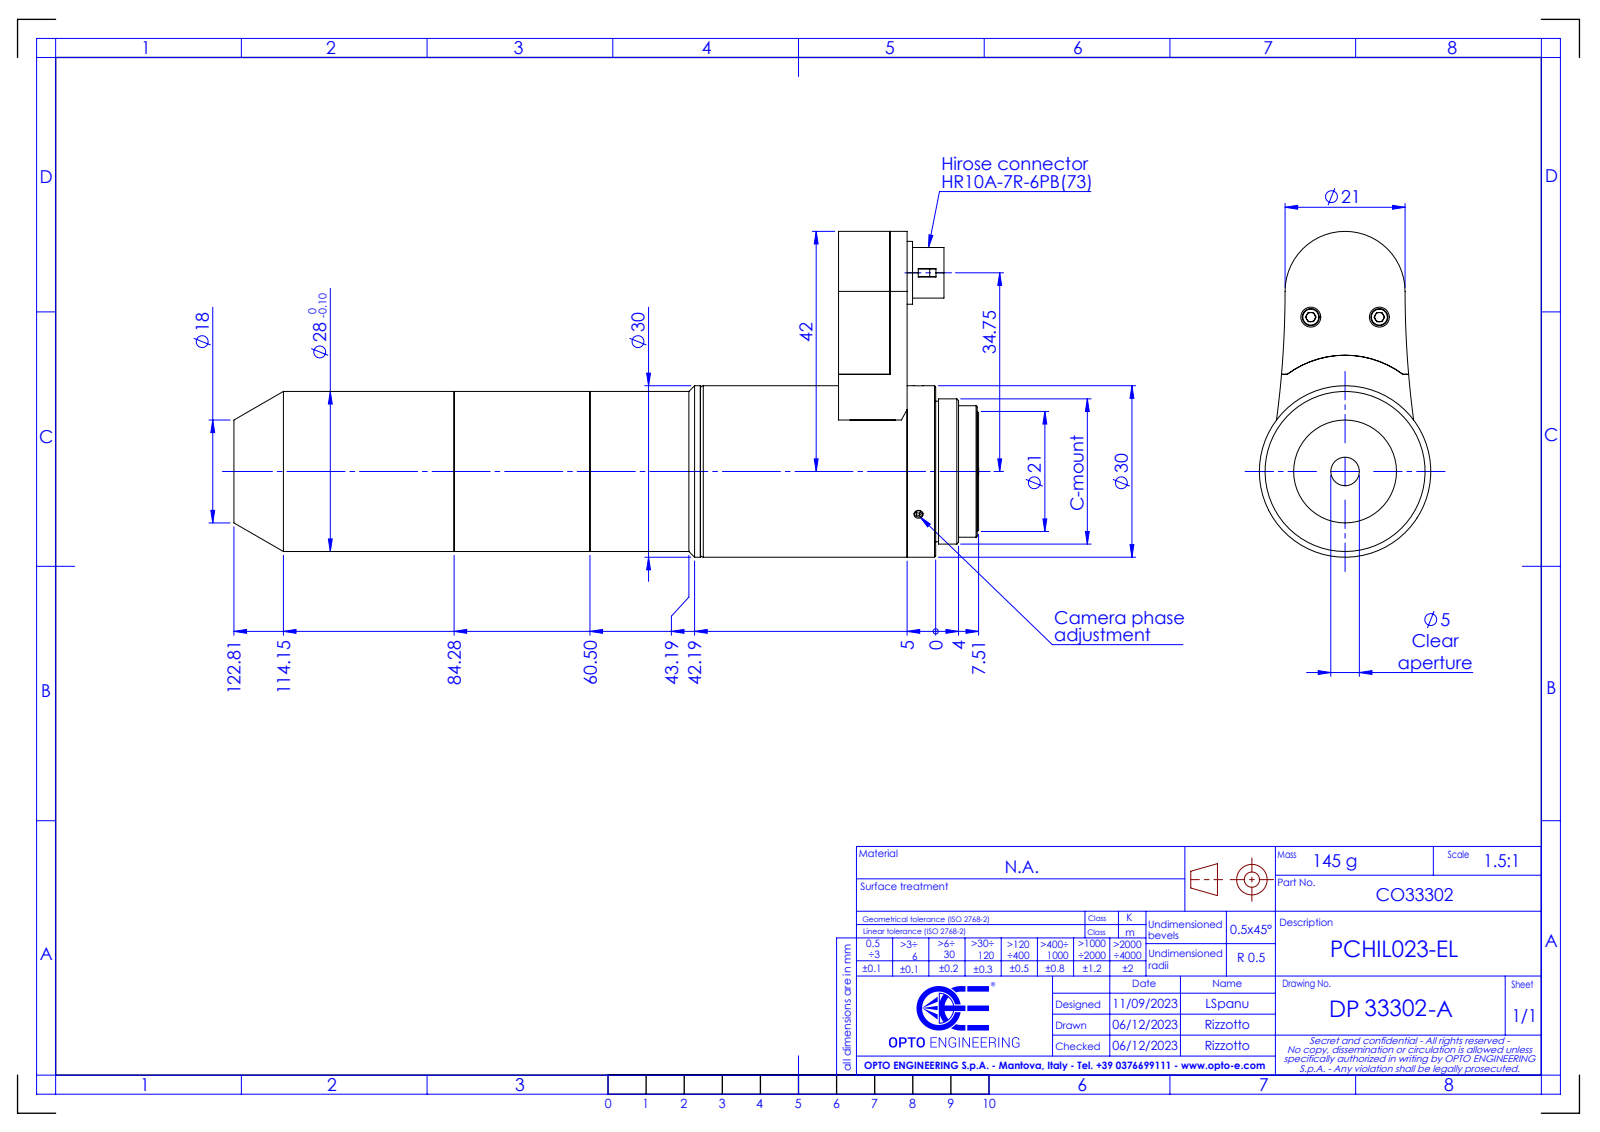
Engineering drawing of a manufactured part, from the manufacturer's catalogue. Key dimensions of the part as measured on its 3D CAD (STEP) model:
Part name (STEP PRODUCT): DP33302-A_PCHIL023-EL
STEP written by: SolidWorks 2021 (CONFIG_CONTROL_DESIGN)
Units: millimetres
Bodies: 0 solids, 187 faces (71 planar, 78 cylindrical, 38 other)
Overall size (bounding box): 130.33 × 57 × 30
Round holes (diameter × count): ⌀1.6 ×3, ⌀1.5 ×2, ⌀3.5 ×2, ⌀5 ×1, ⌀7.4 ×1, ⌀10 ×1
Round bosses / shafts (diameter × count): ⌀1.2 ×2, ⌀30 ×1, ⌀28 ×1, ⌀25.4 ×1, ⌀24.6 ×1, ⌀23 ×1, ⌀21 ×1, ⌀11 ×1
Partial cylindrical surfaces — rounded edges, fillets, slot ends (radius × count): R169.5 ×2, R3.6 ×1, R3.9 ×1, R4 ×1, R10.5 ×1
Main face-to-face distances: 12, 105.81, 117.81, 130.31, 24.5, 12.5, 122.81, 17, 5, 7.5
Hole centre spacings: 7.9, 9.8, 20.02, 27.66, 35.41, 12, 15.8, 26.85
